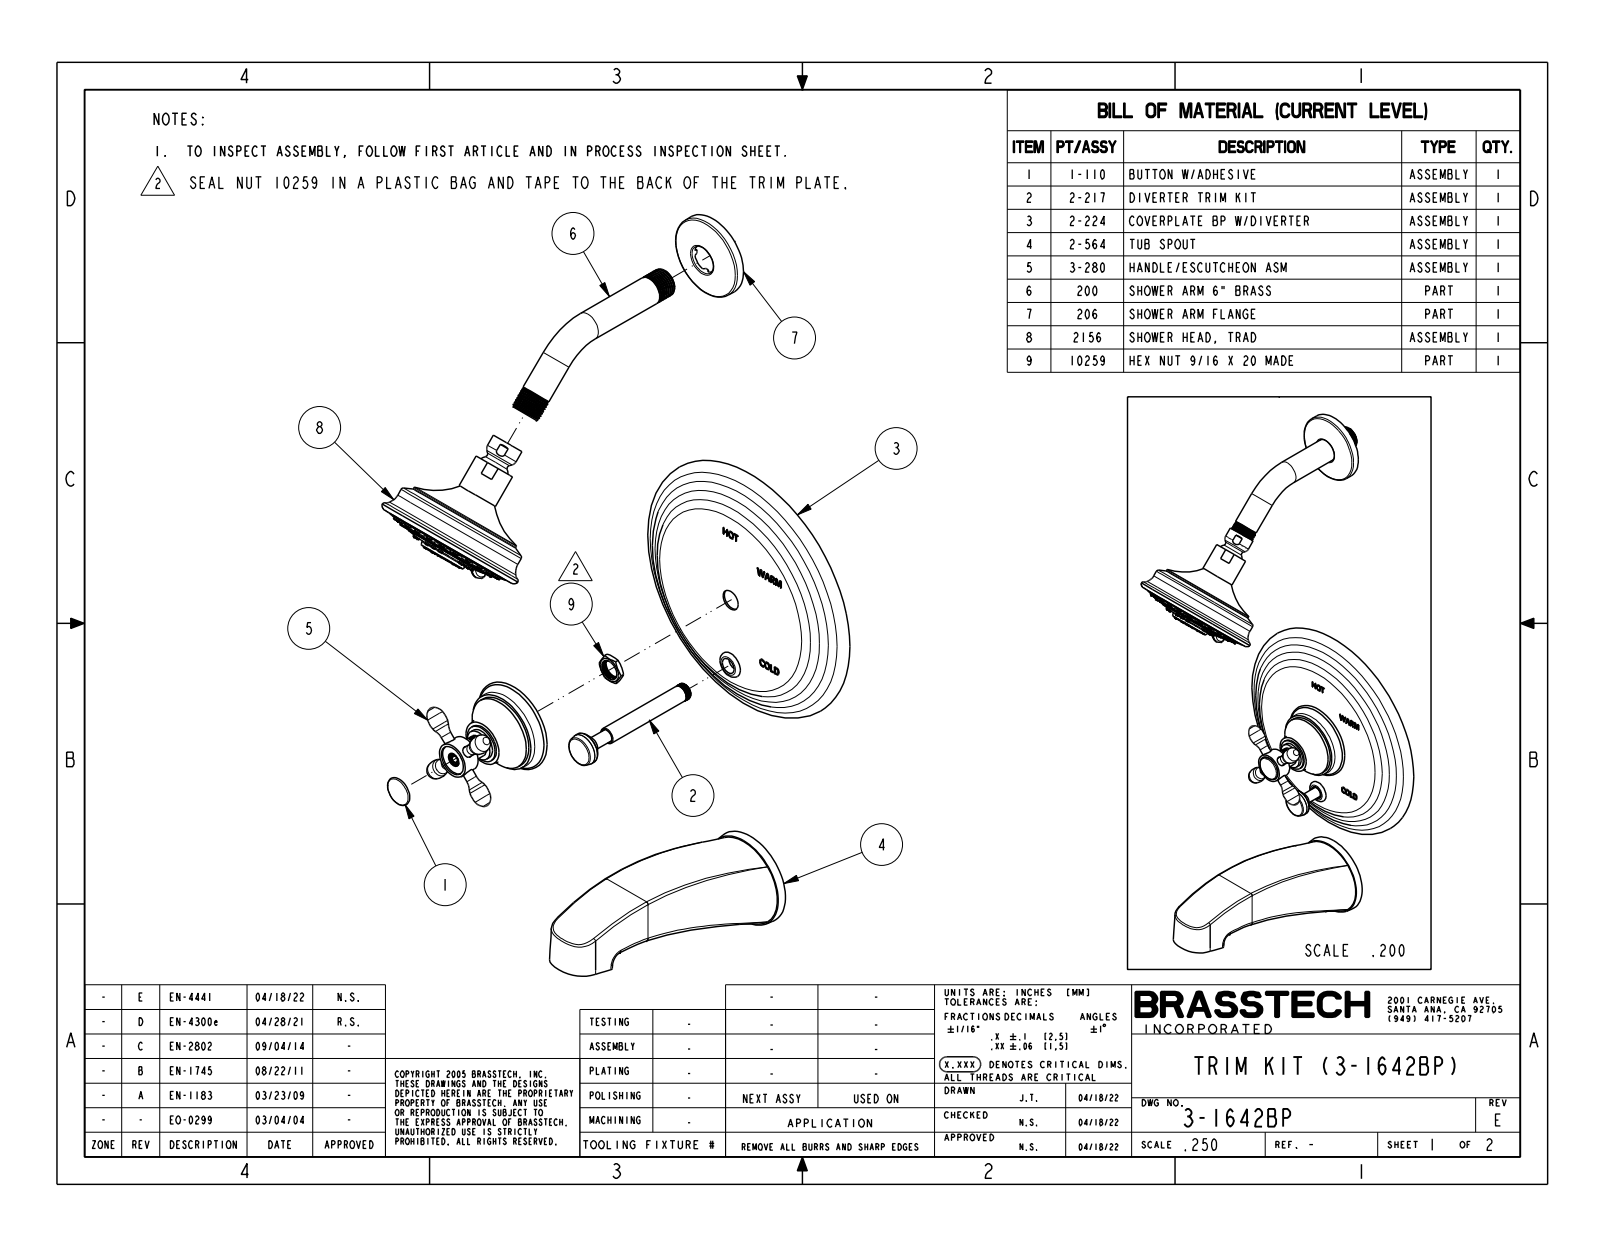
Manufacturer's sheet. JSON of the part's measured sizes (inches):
{"part_name": "3-1642BP", "step_written_by": "CREO PARAMETRIC BY PTC INC, 2018400 (CONFIG_CONTROL_DESIGN)", "units": "inches", "bodies": {"solids": 4, "faces": 1382, "planar": 248, "cylindrical": 228, "other": 906}, "overall_size": [20.565, 8.25, 7.75], "volume_in3": 75.5, "surface_area_in2": 252.3, "round_holes": [[0.059, 8], [0.313, 2], [0.85, 1], [0.925, 1]], "round_bosses_or_shafts": [[0.142, 39], [0.165, 23], [0.813, 2], [0.3, 2], [3.81, 1], [3.724, 1], [3.24, 1], [2.38, 1]], "partial_cylinders_radius": [[0.079, 8], [0.02, 2], [0.138, 1], [0.472, 1], [0.512, 1], [0.63, 1]], "face_to_face_distances": [0.754, 1.12, 0.063, 3.099, 2.345, 1.178, 0.05, 0.118, 0.181, 1.229], "hole_center_spacings": [0.443, 0.579, 0.818, 0.819, 1.069, 0.443, 0.578, 1.069]}
